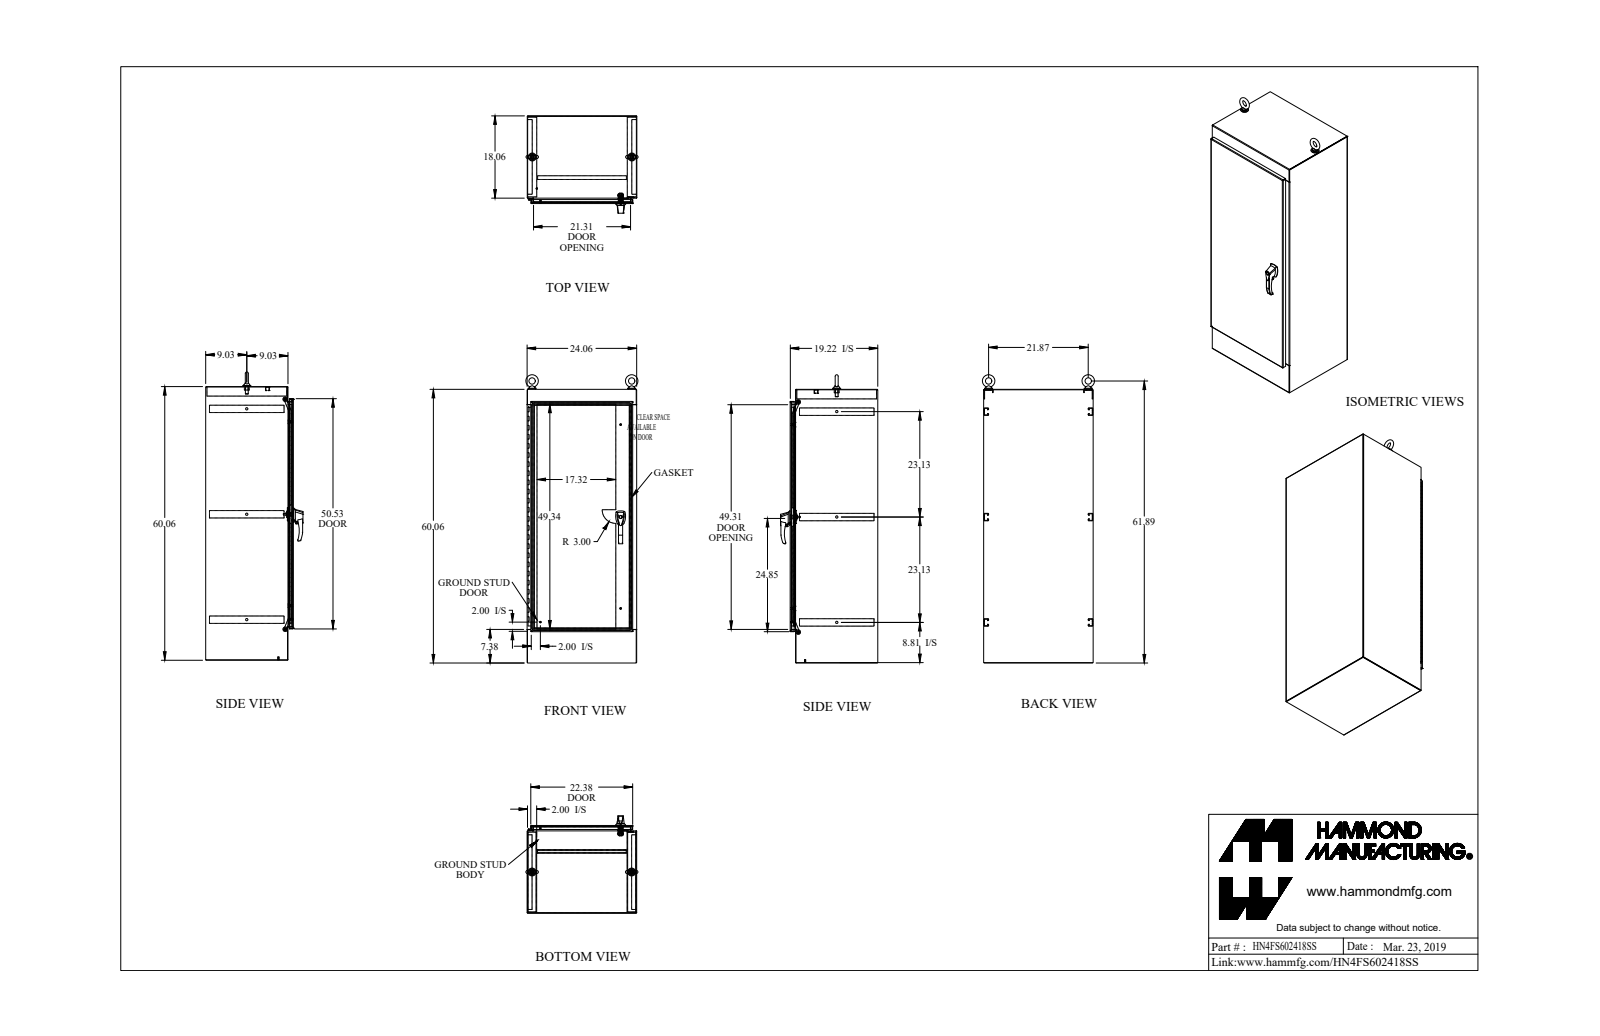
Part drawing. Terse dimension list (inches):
name: HN4FS602418SS
written by: SolidWorks 2018 (AUTOMOTIVE_DESIGN)
unit: in
bodies: 51 solids, 1611 faces (735 planar, 713 cylindrical, 163 other)
size: 63.256 × 24.604 × 21.362
volume: 695.6 in³; area: 14 601 in²
holes: 8× ⌀0.304, 3× ⌀0.5, 2× ⌀0.25, 2× ⌀0.257, 2× ⌀0.28, 2× ⌀0.281, 2× ⌀0.313, 2× ⌀0.39, 2× ⌀0.413, 2× ⌀0.527, 2× ⌀0.625, 2× ⌀0.68
bosses: 2× ⌀1.75, 2× ⌀1.5, 2× ⌀1.25, 2× ⌀1, 2× ⌀0.75, 2× ⌀0.738, 2× ⌀0.63, 2× ⌀0.625
rounds: 42× R0.043, 36× R0.138, 22× R0.125, 16× R0.017, 15× R0.048, 15× R0.143, 10× R0.06, 7× R0.318
face distances: 0.095, 19.152, 23.965, 23.87, 19.057, 19.247, 24.06, 59.965, 17.965, 1.187
hole spacings: 6, 12, 18, 24, 30, 1.126, 1.287, 19.681
